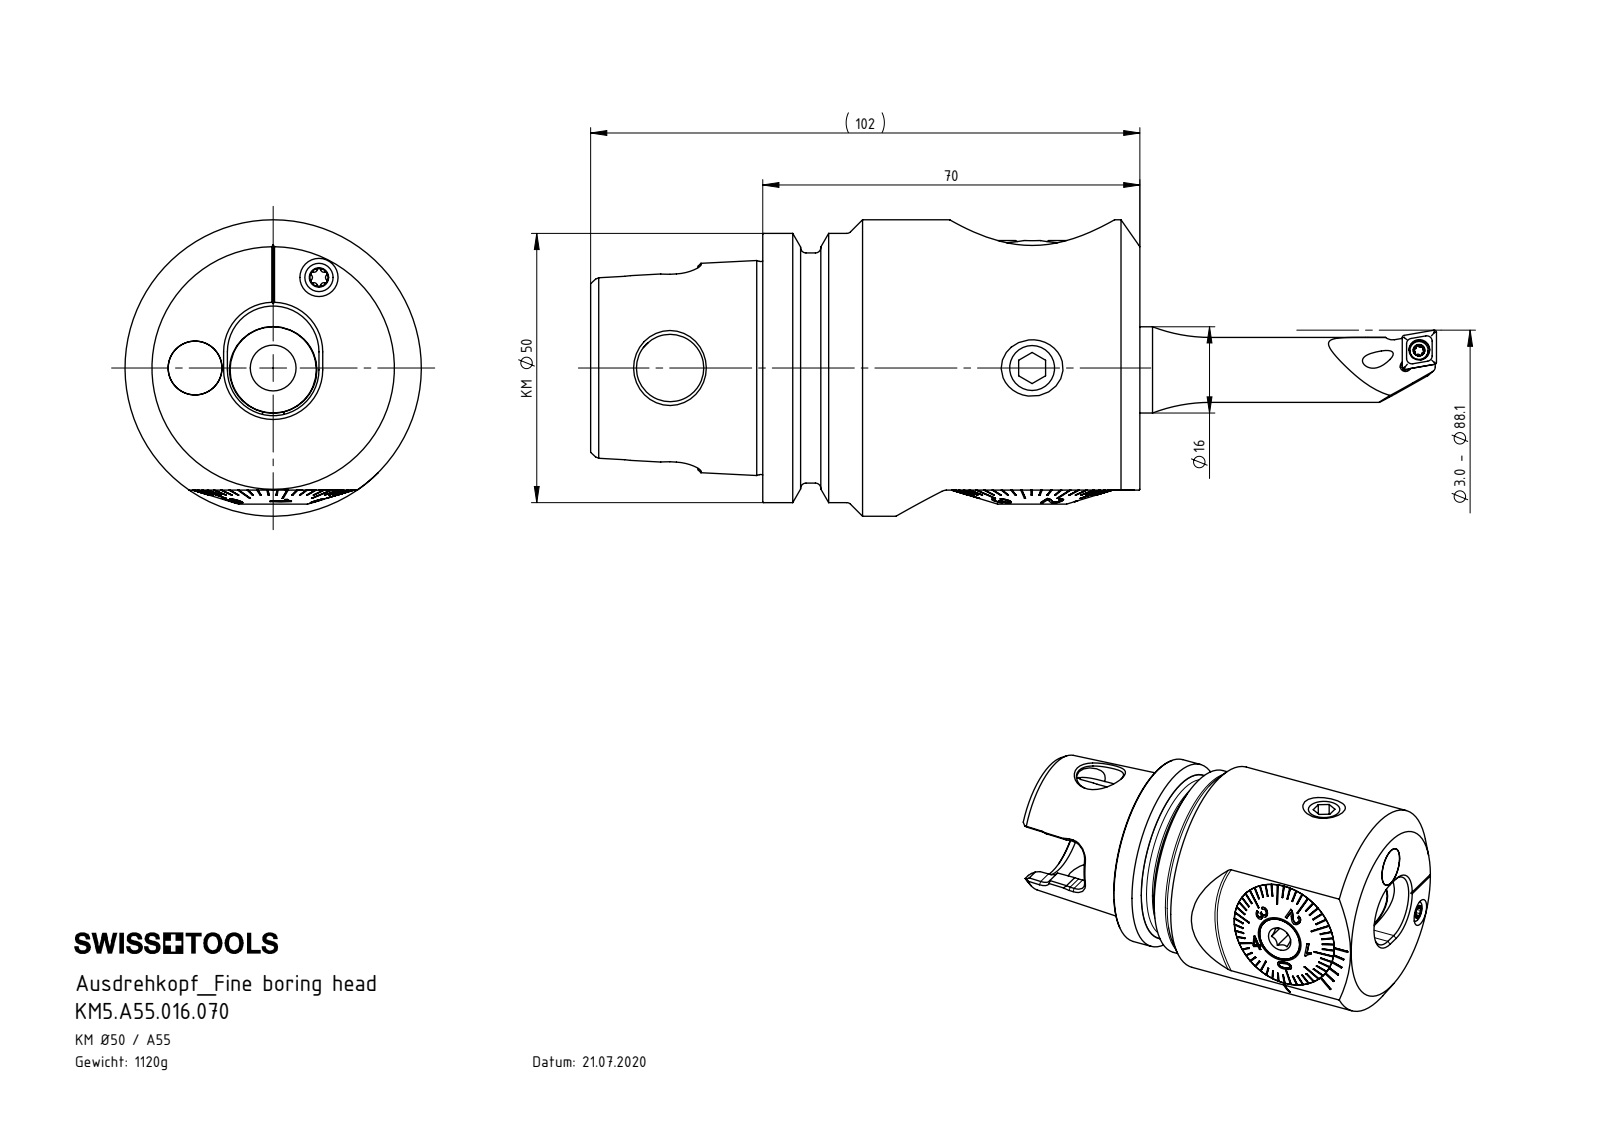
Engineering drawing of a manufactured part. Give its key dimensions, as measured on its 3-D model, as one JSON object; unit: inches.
{"part_name": "A55-BG1.012.007_C; A55-BG2.013.005_C; KM5.A55.AA4.070; A55-BG2.012.006_B (+8 more)", "step_written_by": "SolidWorks 2017 (AUTOMOTIVE_DESIGN)", "units": "inches", "bodies": {"solids": 14, "faces": 652, "planar": 336, "cylindrical": 98, "other": 218}, "overall_size": [4.014, 2.165, 2.165], "volume_in3": 8.598, "surface_area_in2": 68.39, "round_holes": [[0.335, 4], [0.063, 1], [0.13, 1], [0.165, 1], [0.315, 1], [0.394, 1], [0.449, 1], [0.488, 1], [0.492, 1], [0.551, 1], [0.559, 1], [0.63, 1]], "round_bosses_or_shafts": [[0.394, 3], [2.165, 1], [1.967, 1], [1.681, 1], [1.181, 1], [1.18, 1], [1.177, 1], [0.984, 1]], "partial_cylinders_radius": [[0.013, 6], [0.023, 6], [0.157, 6], [0.055, 4], [0.075, 4], [0.126, 3], [0.079, 2], [0.238, 2]], "face_to_face_distances": [0.197, 0.209, 0.11, 0.098, 0.256, 0.146, 0.047, 2.756, 0.02, 2.736], "hole_center_spacings": [0.571, 0.285, 0.014, 0.741, 0.754, 1.121, 2.646]}
